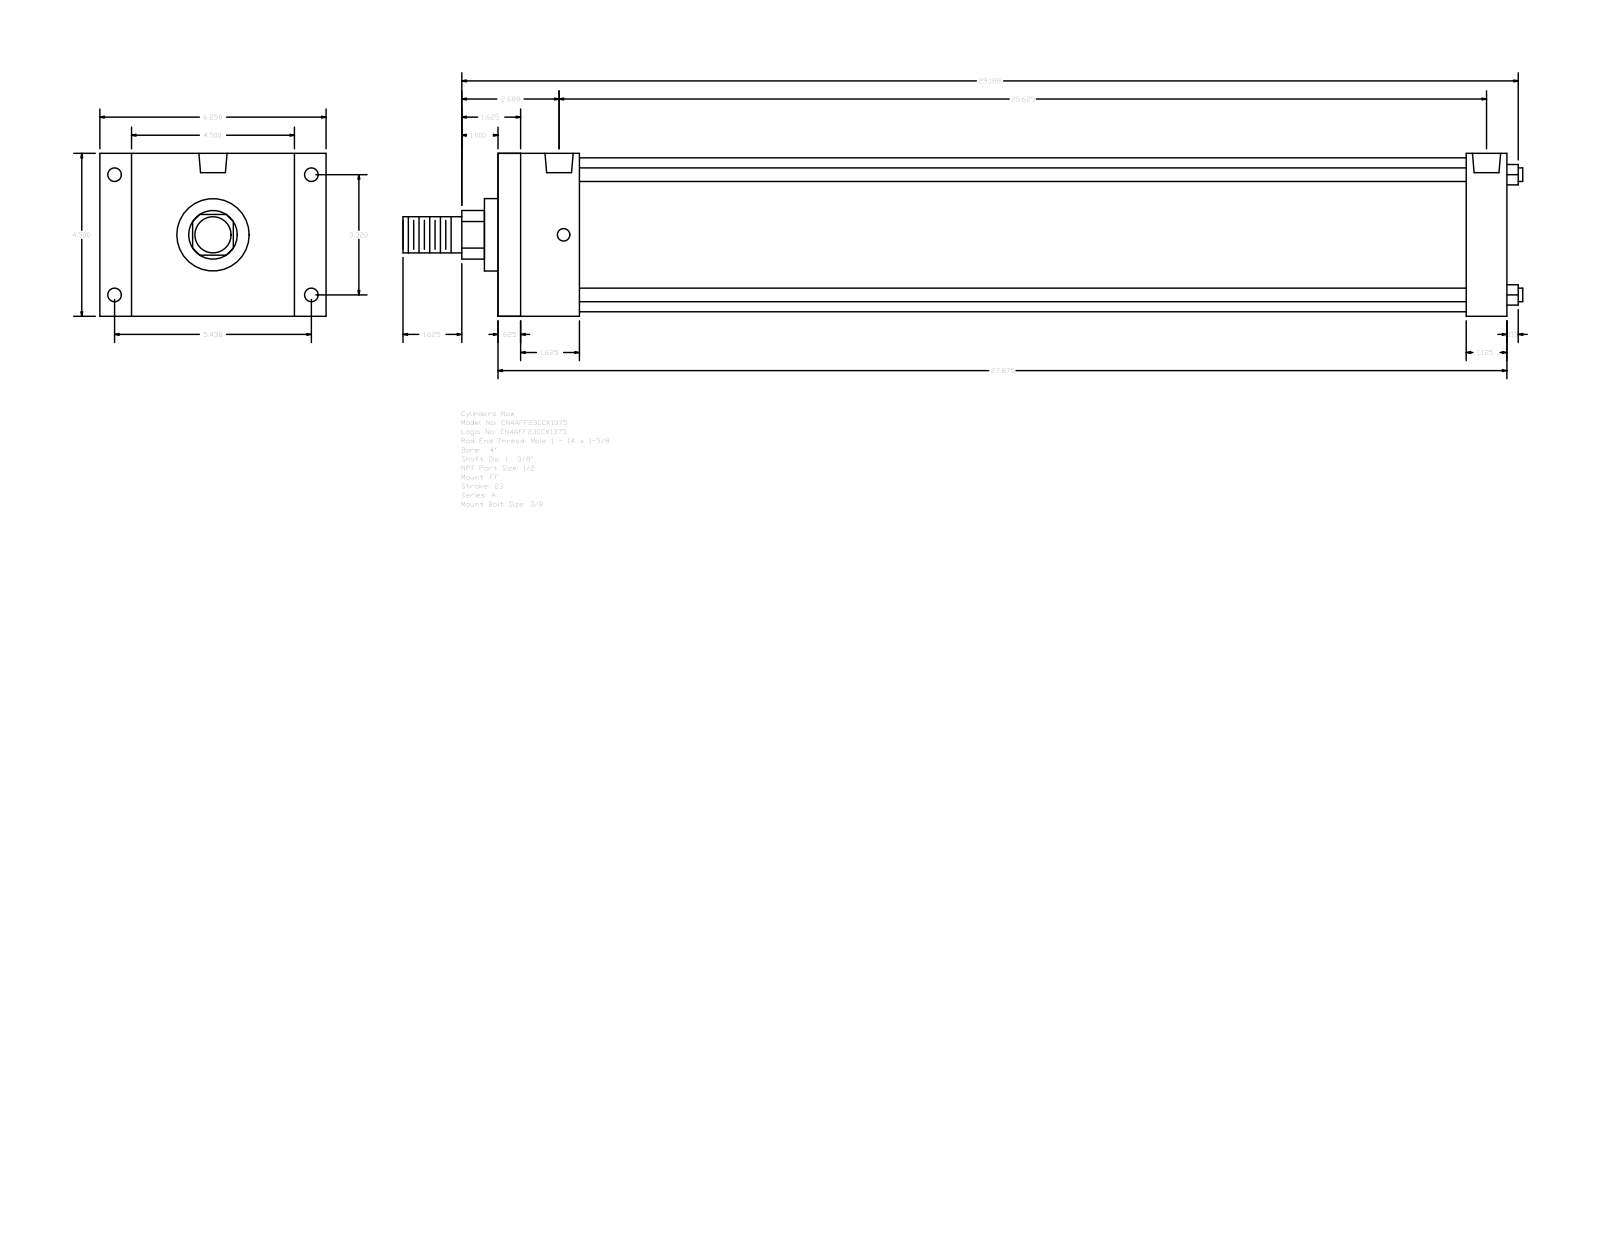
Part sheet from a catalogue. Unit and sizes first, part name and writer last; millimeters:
Units: millimetres
Overall size (bounding box): 785.81 × 158.75 × 114.3
Round holes (diameter × count): ⌀8.73 ×4, ⌀9.53 ×4, ⌀19.77 ×2
Round bosses / shafts (diameter × count): ⌀9.53 ×4, ⌀107.95 ×1, ⌀50.8 ×1, ⌀34.92 ×1, ⌀25.4 ×1
Partial cylindrical surfaces — rounded edges, fillets, slot ends (radius × count): R17.06 ×1
Main face-to-face distances: 114.3, 708.02, 692.15, 15.87, 57.15, 28.57, 22.23, 136.53, 679.45, 663.58
Hole centre spacings: 3.18, 84.32, 138.12, 161.82, 644.52, 647.7, 650.88
Bodies: 0 solids, 92 faces (64 planar, 28 cylindrical, 0 other)
Part name (STEP PRODUCT): A_FF__0400_1.375
STEP written by: GSSL Pune (CONFIG_CONTROL_DESIGN)
